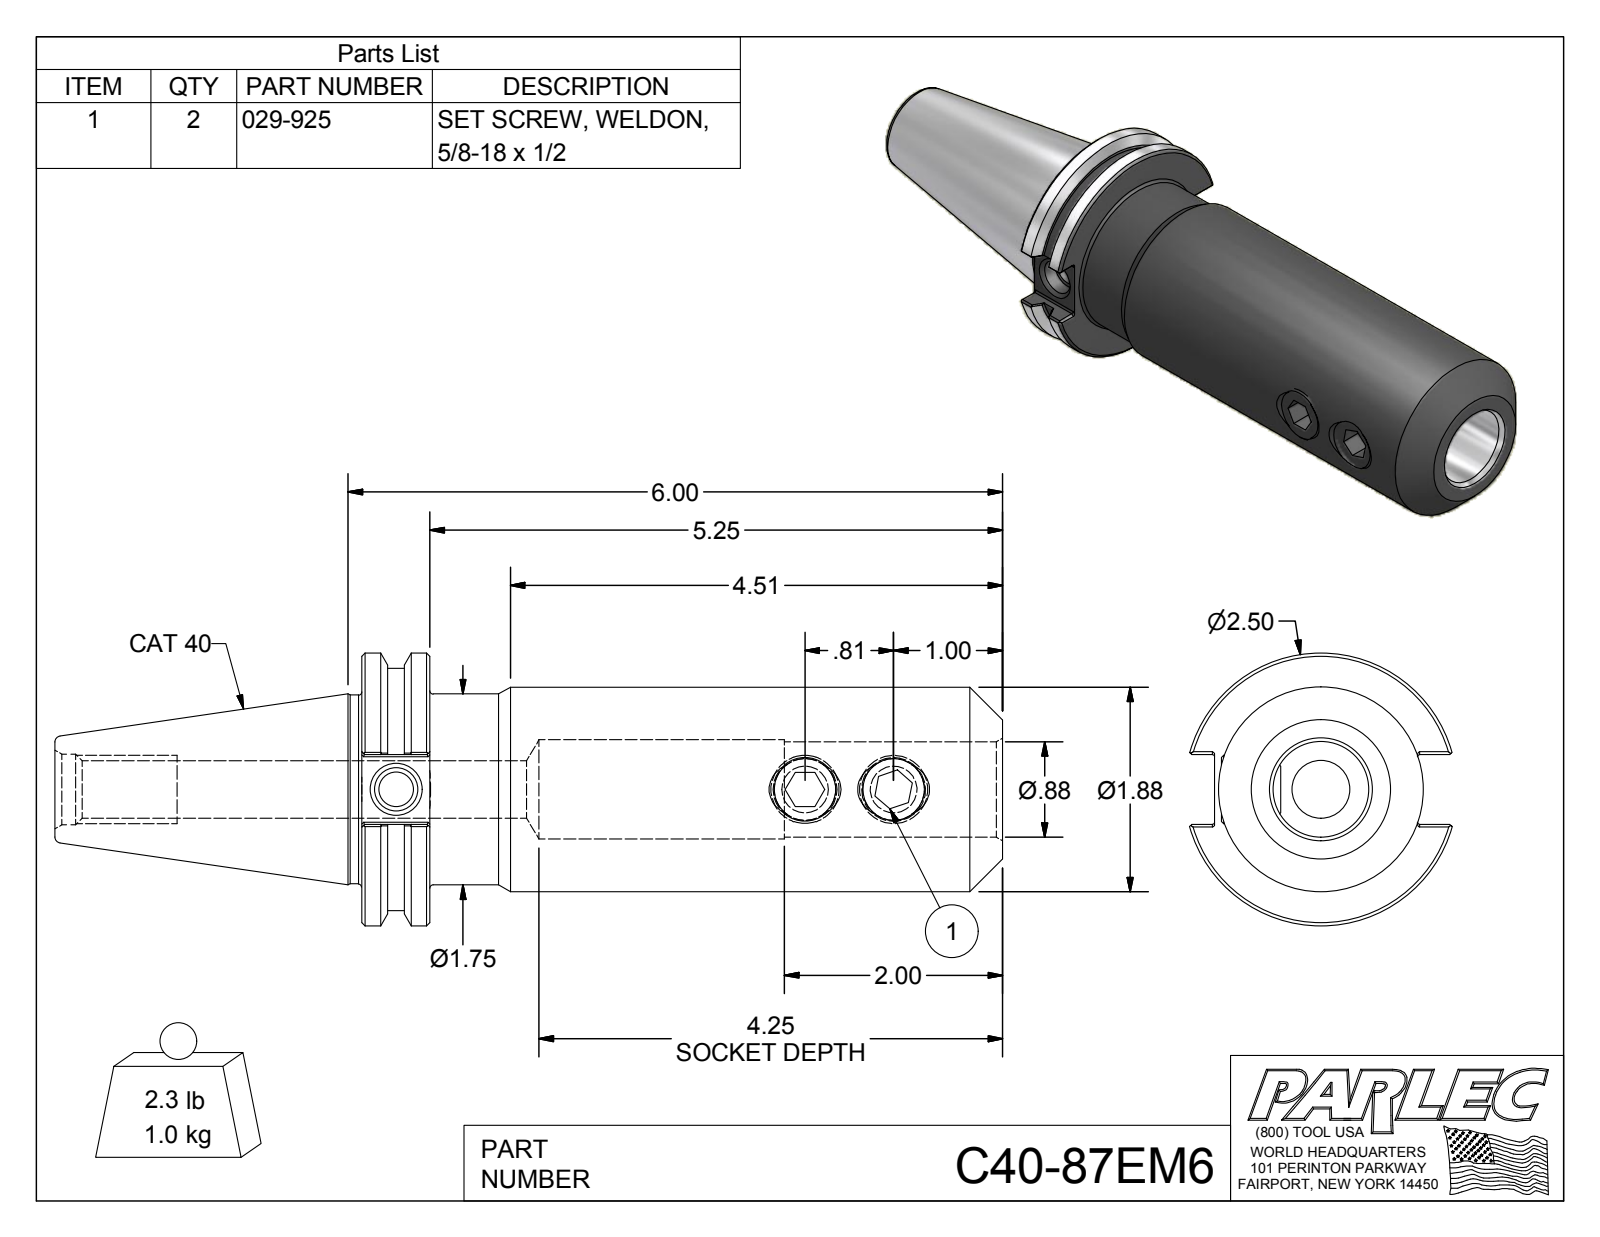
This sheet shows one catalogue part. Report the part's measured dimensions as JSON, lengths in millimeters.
{"part_name": "C40-87EM6; C40-87EM6-1; 029-925", "step_written_by": "Autodesk Inventor 2012 (AUTOMOTIVE_DESIGN)", "units": "millimeters", "bodies": {"solids": 3, "faces": 118, "planar": 50, "cylindrical": 31, "other": 37}, "overall_size": [220.6, 63.5, 61.1], "volume_mm3": 281700, "surface_area_mm2": 51100, "round_holes": [[14.4, 2], [8, 1], [10.1, 1], [13.4, 1], [16.5, 1], [22.2, 1], [23.1, 1]], "round_bosses_or_shafts": [[15.9, 2], [63.5, 1], [56.4, 1], [47.6, 1], [44.5, 1], [43.9, 1]], "partial_cylinders_radius": [[0.5, 12]], "face_to_face_distances": [15.9, 149.2, 133.4, 1.1, 8, 12.7, 16.3, 47.2, 71.4, 87.3], "hole_center_spacings": [20.6, 95.2, 115.8]}
